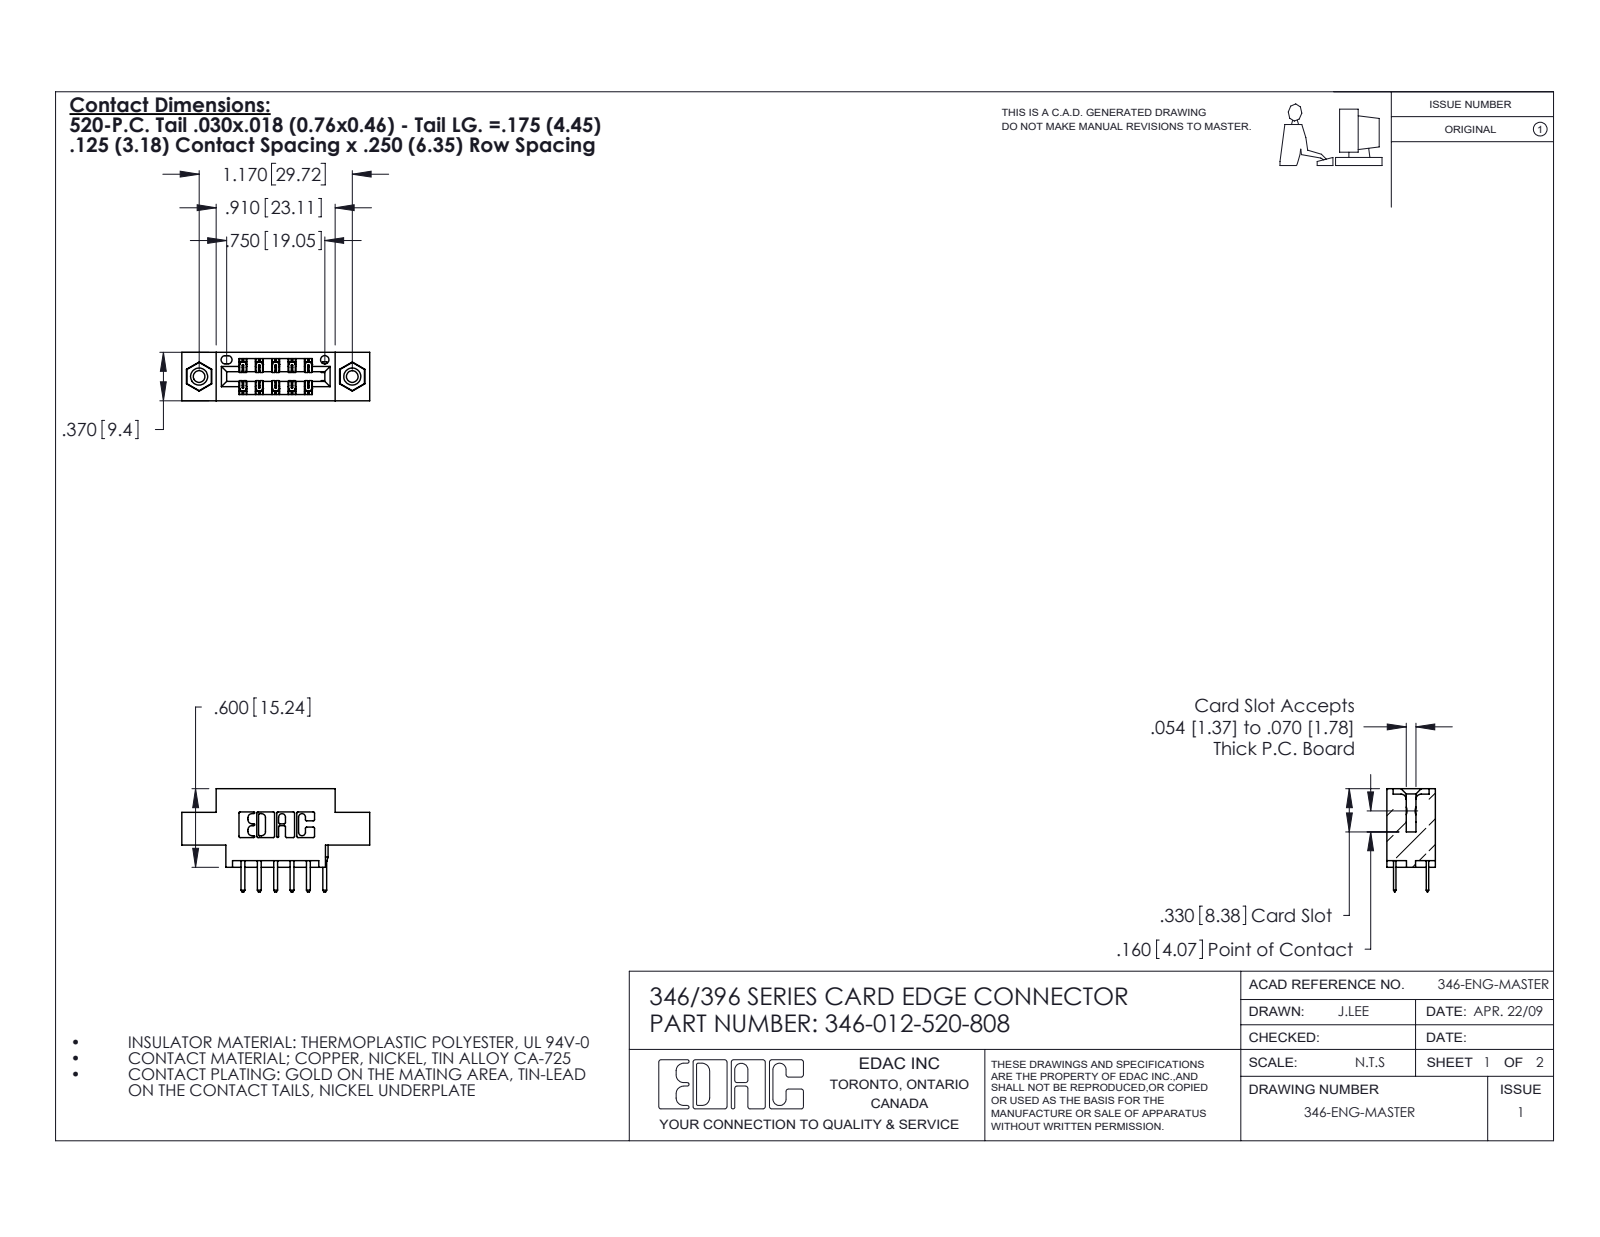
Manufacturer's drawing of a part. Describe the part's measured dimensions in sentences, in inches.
The part is named "345-292-001_345-293-120; 346-012-520-808; 346 Part_0.170 Offset - 0.156 Dia-TI; 345-250-001_345-250-003-102". Its 3-D file was written by "SolidWorks 2020 (CONFIG_CONTROL_DESIGN)". It is 15 solids with 846 faces: 546 planar, 284 cylindrical and 16 other. Overall it measures 1.435 by 0.788 by 0.37 inches. Its volume is 0.19 cubic inches and its surface area 6.194 square inches. Round holes: 2 of diameter 0.089, 2 of diameter 0.125, 2 of diameter 0.156, 1 of diameter 0.064. Round bosses or shafts: 2 of diameter 0.155. Partial cylindrical surfaces (rounded edges, fillets, slot ends): 22 of radius 0.01, 18 of radius 0.006, 16 of radius 0.01, 6 of radius 0.007, 6 of radius 0.031, 3 of radius 0.026, 2 of radius 0.014, 2 of radius 0.022. The main face-to-face distances are 0.25, 0.37, 0.048, 0.322, 0.222, 0.148, 0.1, 0.174, 0.072, 0.298. The hole center spacings are 0.246, 0.969, 1.17.
